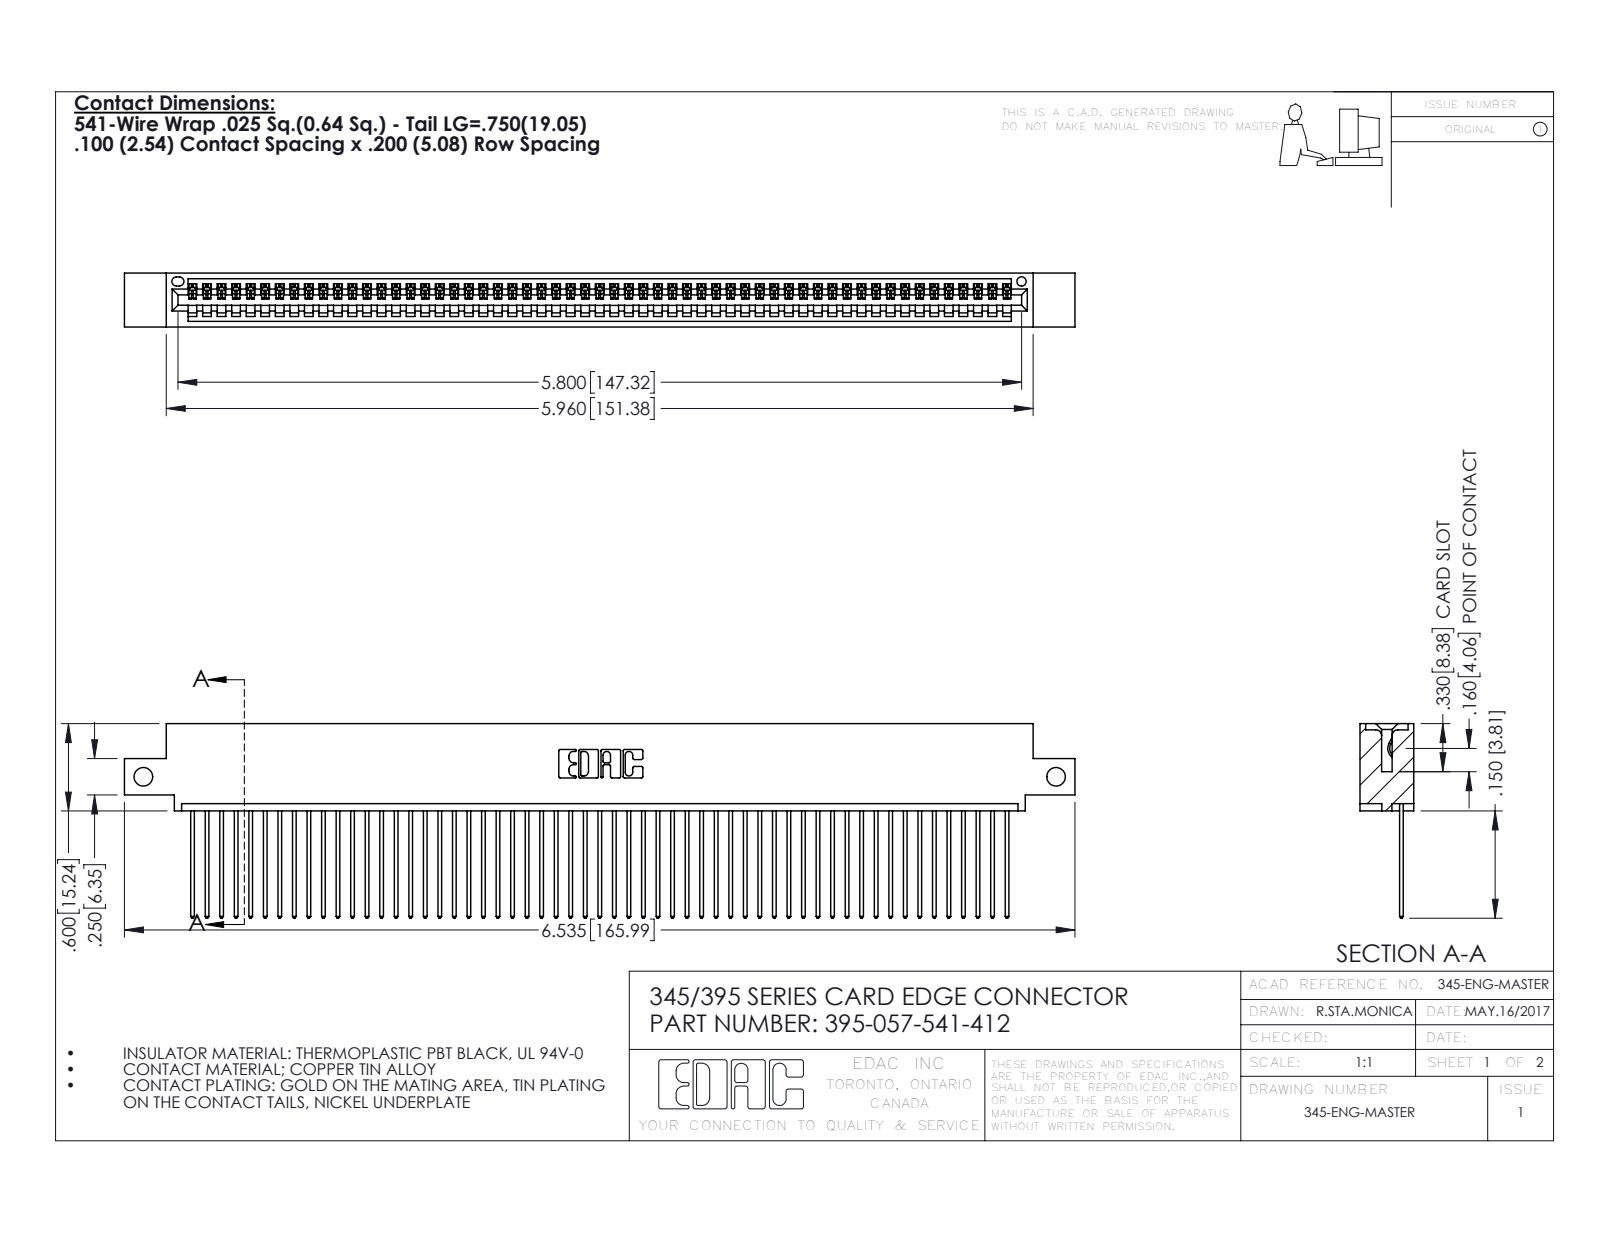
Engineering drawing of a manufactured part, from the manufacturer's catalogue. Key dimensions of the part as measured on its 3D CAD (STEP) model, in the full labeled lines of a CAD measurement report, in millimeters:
Part name (STEP PRODUCT): 345 Part_0.110 Offset - Side Mount; 395-057-541-412; 345-292-001_345-293-141
STEP written by: SolidWorks 2016 (CONFIG_CONTROL_DESIGN)
Units: millimetres
Bodies: 58 solids, 3436 faces (2364 planar, 1072 cylindrical, 0 other)
Overall size (bounding box): 166 × 34 × 9.4
Volume: 15 900 mm³ · Surface area: 22 400 mm²
Round holes (diameter × count): ⌀3.3 ×2, ⌀1.6 ×1
Partial cylindrical surfaces — rounded edges, fillets, slot ends (radius × count): R0.2 ×114, R0.3 ×114, R0.3 ×22, R0.2 ×6, R0.8 ×6, R0.7 ×3, R0.8 ×2, R1 ×2
Main face-to-face distances: 1.8, 7.6, 2.5, 6.9, 0.6, 9.4, 5.1, 5.7, 3.8, 1.8
Hole centre spacings: 159.4
